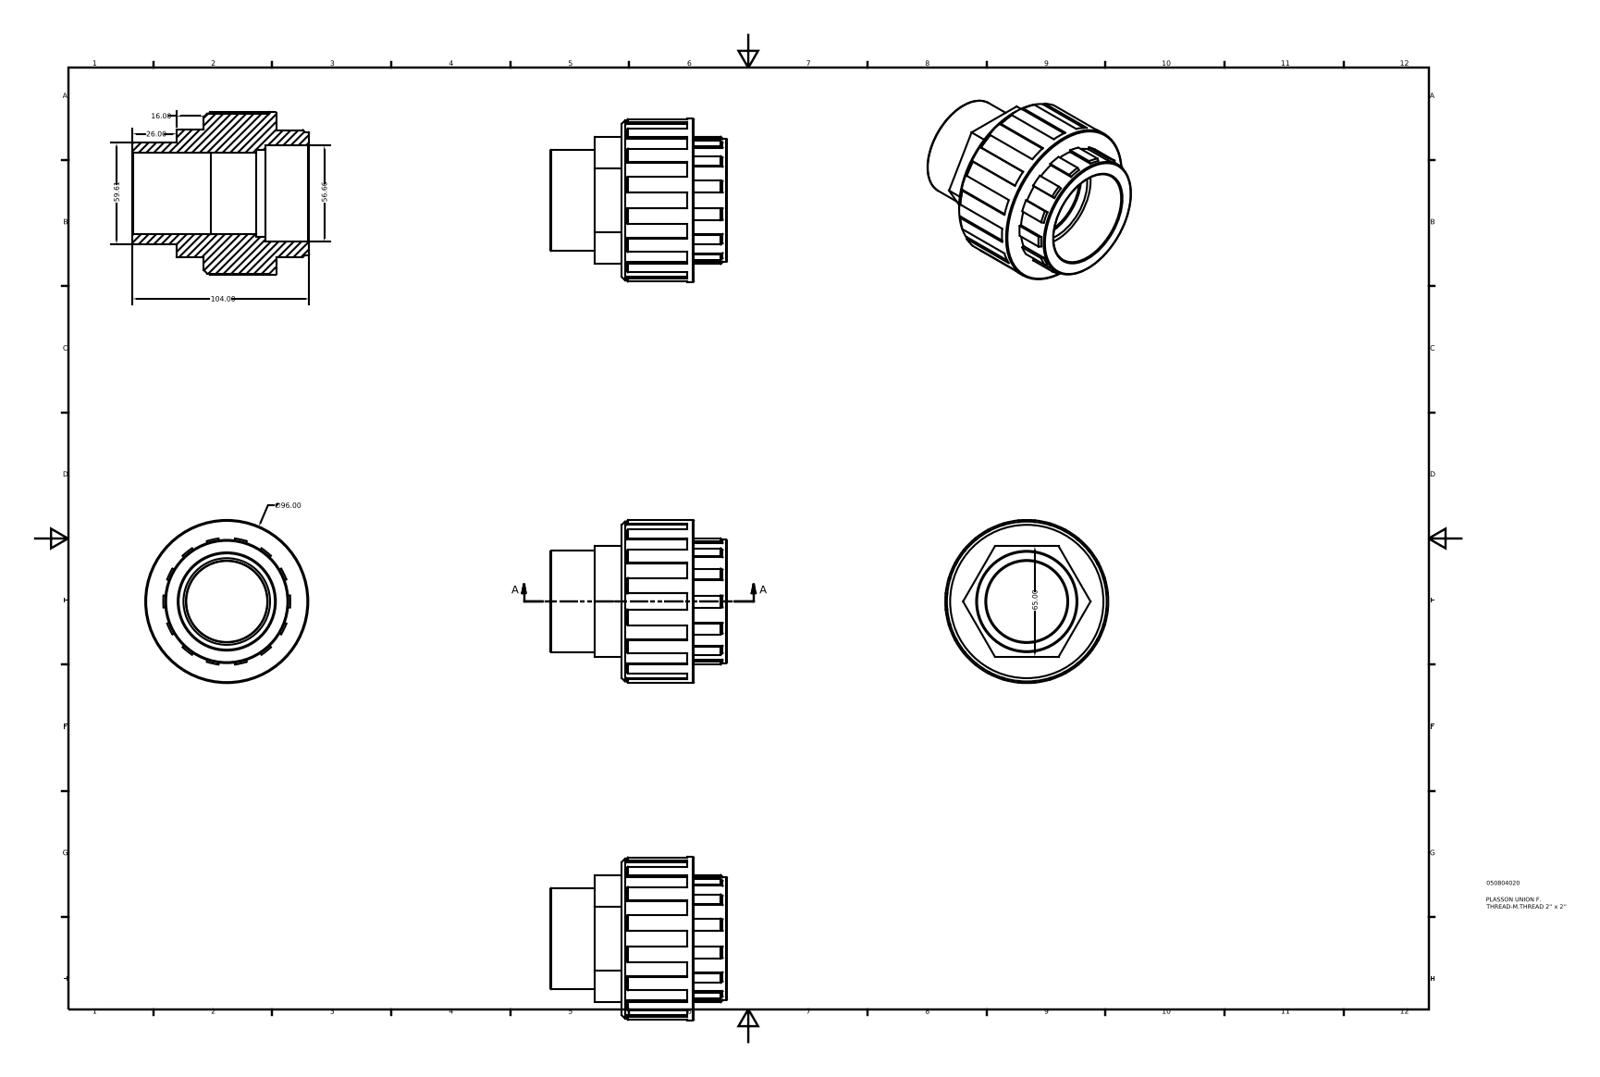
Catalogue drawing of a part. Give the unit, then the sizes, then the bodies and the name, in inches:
Units: inches
Overall size (bounding box): 4.094 × 3.78 × 3.78
Round holes (diameter × count): ⌀1.878 ×1, ⌀1.896 ×1, ⌀2.007 ×1, ⌀2.231 ×1
Round bosses / shafts (diameter × count): ⌀3.78 ×1, ⌀3.704 ×1, ⌀2.855 ×1, ⌀2.347 ×1
Partial cylindrical surfaces — rounded edges, fillets, slot ends (radius × count): R1.472 ×1
Main face-to-face distances: 1.673, 2.559, 2.441, 0.768, 3.071, 1.024, 0.63, 2.303, 1.654, 3.327
Volume: 18.75 in³ · Surface area: 83.44 in²
Bodies: 1 solid, 148 faces (90 planar, 22 cylindrical, 36 other)
Part name (STEP PRODUCT): 050804020
STEP written by: Autodesk Inventor 2015 (AUTOMOTIVE_DESIGN)
